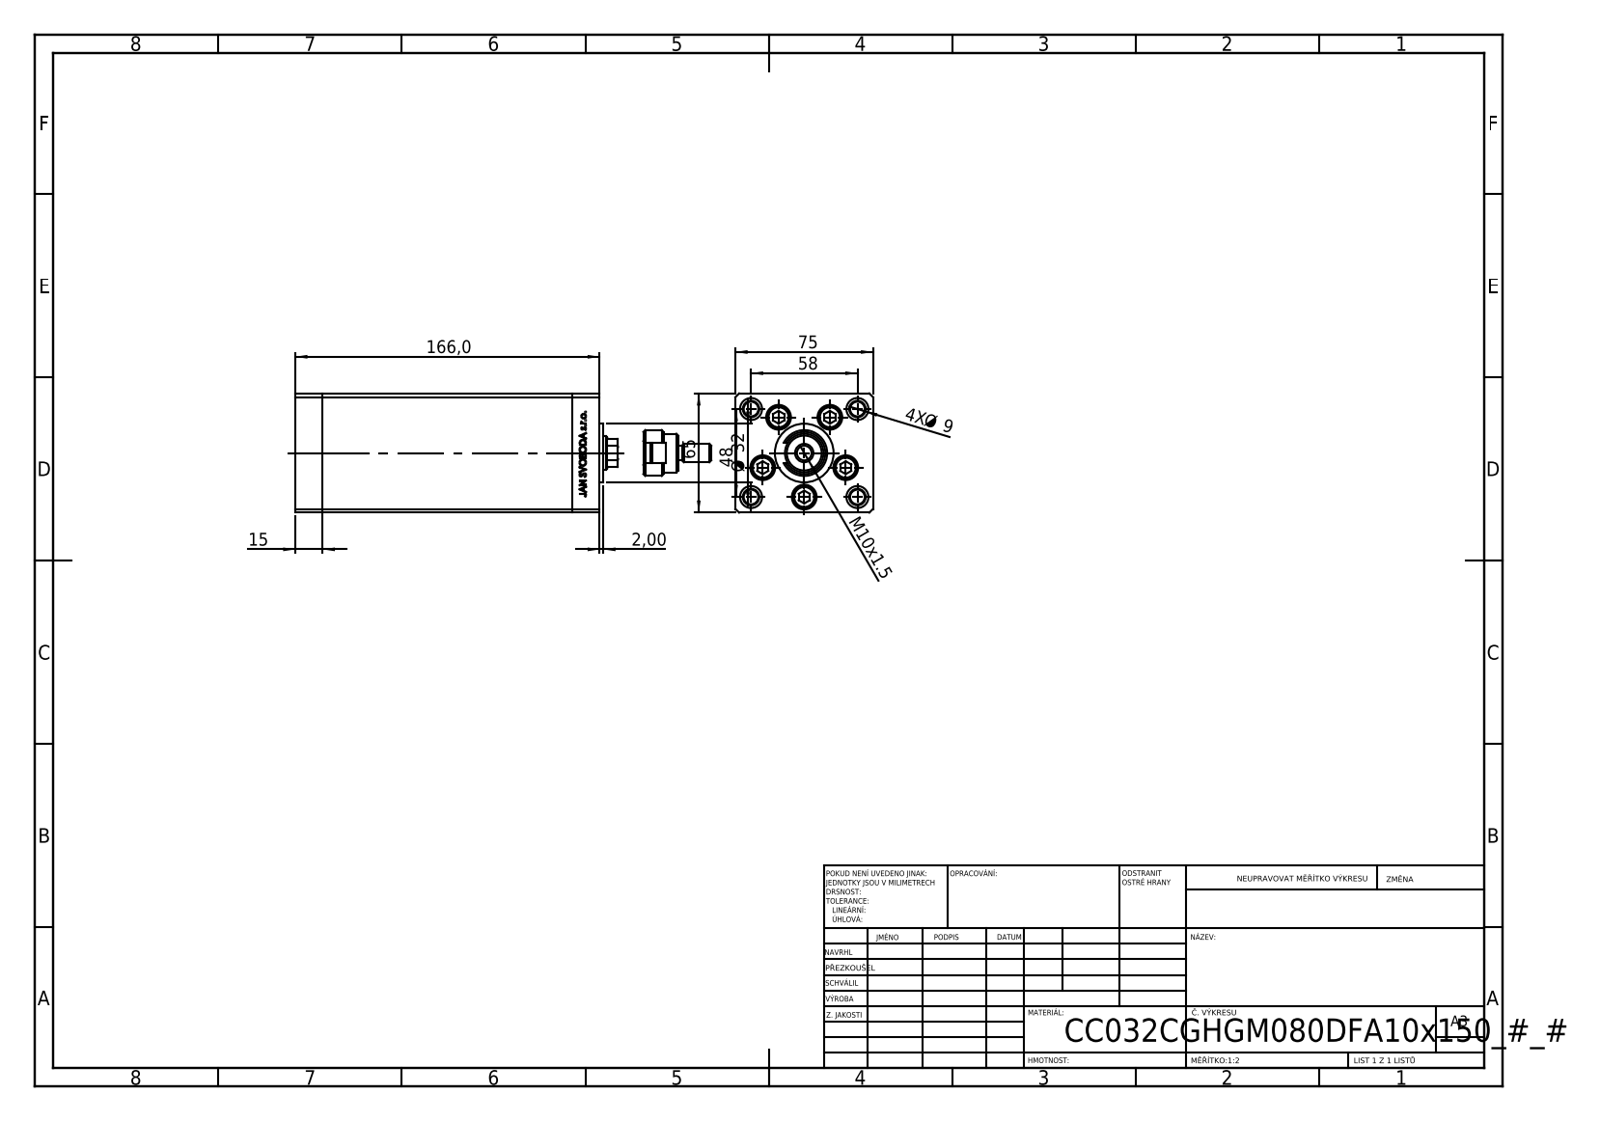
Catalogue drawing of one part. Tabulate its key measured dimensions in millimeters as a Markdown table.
| quantity | value |
| --- | --- |
| part name | ALLEN BOLT; FEMALE_PART_FOR_DFA; V220C_VC_C; V220C BACK_C (+2 more) |
| STEP written by | SolidWorks 2019 (CONFIG_CONTROL_DESIGN) |
| units | millimeters |
| bodies | 14 solids, 1212 faces (554 planar, 184 cylindrical, 474 other) |
| overall size | 226.8 × 75 × 65 |
| volume | 683 256 mm³ |
| surface area | 147 102 mm² |
| round holes (diameter × count) | 9 × 9, 13.5 × 5, 2 × 4, 8 × 4, 12 × 4, 13.16 × 4, 8.5 × 1, 12.5 × 1, 18 × 1 |
| round bosses / shafts (diameter × count) | 8 × 6, 12.5 × 4, 32 × 1, 25 × 1, 21 × 1, 10 × 1 |
| partial cylindrical surfaces (radius × count) | 0.93 × 2, 5.5 × 1, 8.5 × 1, 8.75 × 1 |
| main face-to-face distances | 75, 65, 15, 136, 151, 166, 13, 28, 9, 142 |
| hole center spacings | 24, 37.64, 15.67, 17.22, 27.71, 28.83, 29, 32.63 |
